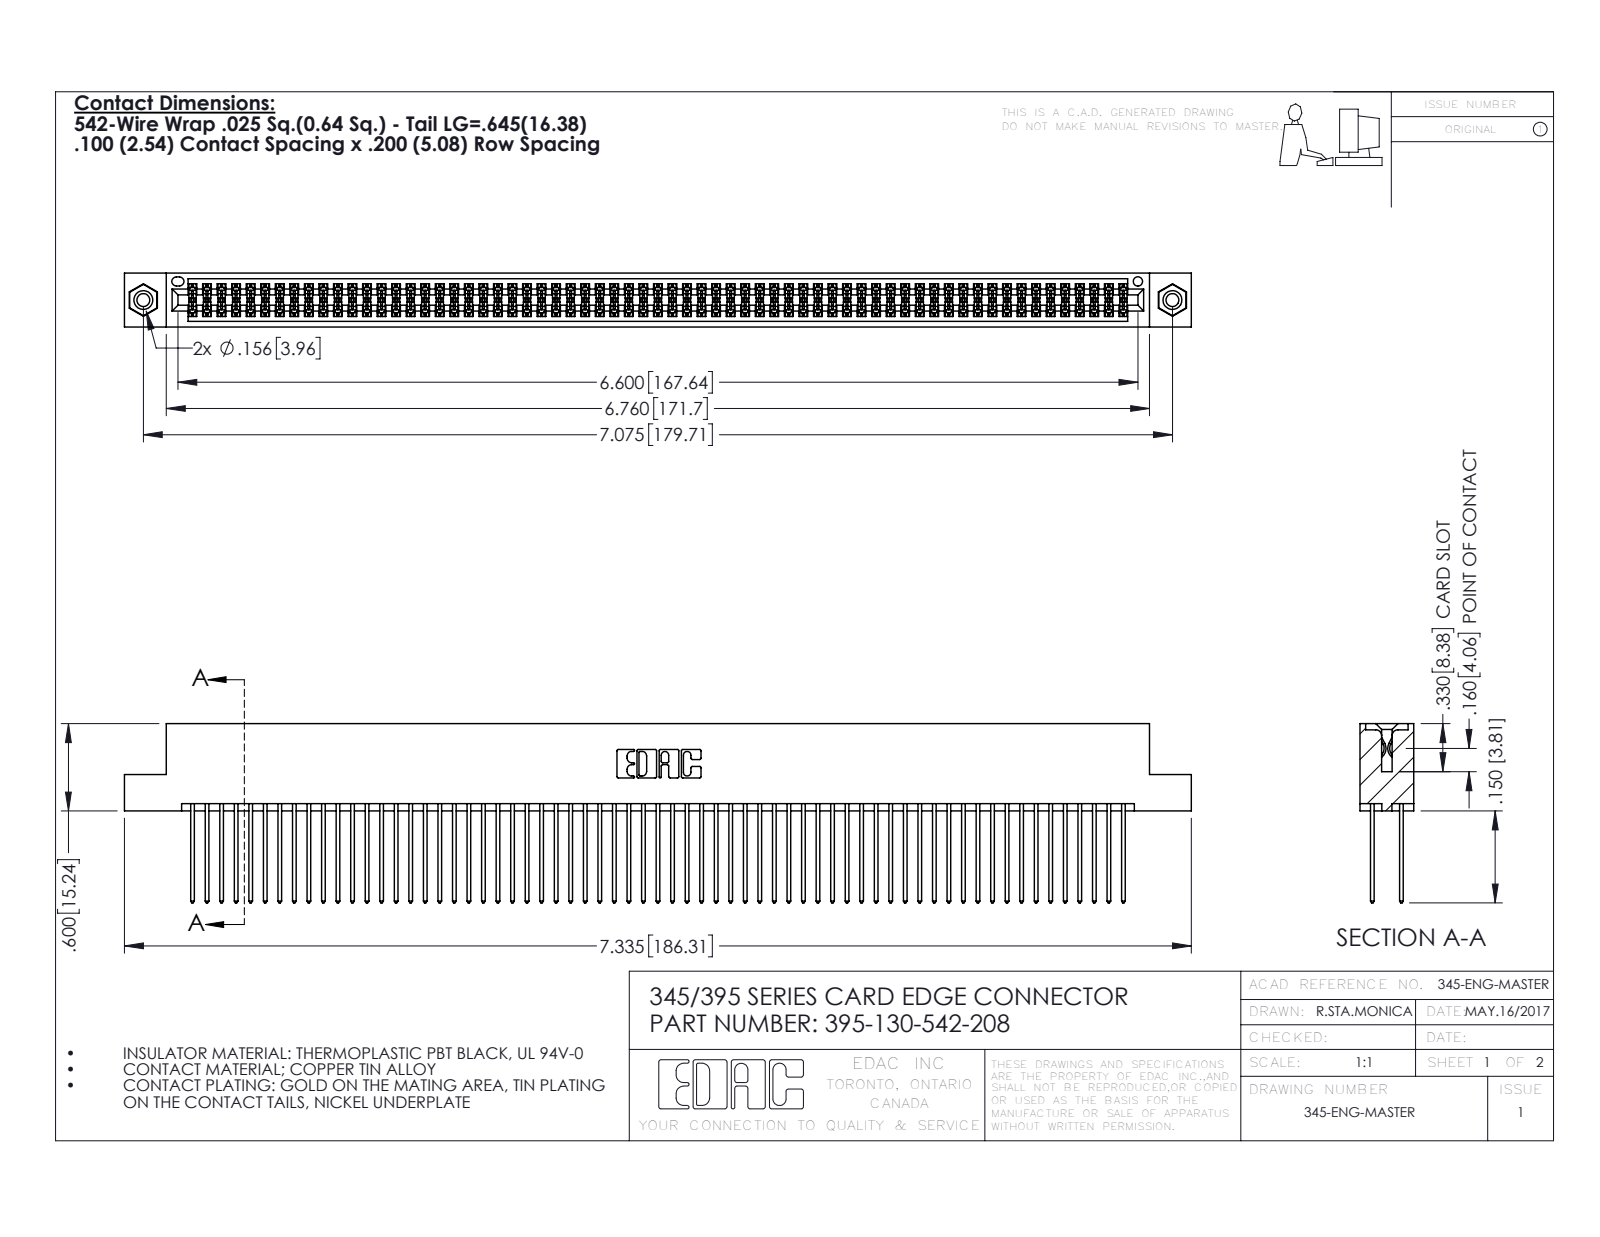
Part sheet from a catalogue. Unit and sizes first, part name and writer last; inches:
Units: inches
Overall size (bounding box): 7.335 × 1.232 × 0.37
Round holes (diameter × count): ⌀0.089 ×2, ⌀0.125 ×2, ⌀0.156 ×2, ⌀0.064 ×1
Round bosses / shafts (diameter × count): ⌀0.155 ×2
Partial cylindrical surfaces — rounded edges, fillets, slot ends (radius × count): R0.006 ×195, R0.01 ×130, R0.01 ×22, R0.007 ×6, R0.031 ×6, R0.026 ×3, R0.014 ×2, R0.019 ×2
Main face-to-face distances: 0.072, 0.298, 0.2, 0.098, 0.272, 0.025, 0.225, 0.37, 0.175, 0.149
Hole centre spacings: 0.27, 6.839, 7.075
Volume: 1.154 in³ · Surface area: 48.43 in²
Bodies: 133 solids, 6686 faces (4402 planar, 2268 cylindrical, 16 other)
Part name (STEP PRODUCT): 345-292-001_345-293-142; 345-250-001_345-250-003-102; 345 Part_Flush Mounting Lugs - 0.156 Dia-TI; 395-130-542-208
STEP written by: SolidWorks 2016 (CONFIG_CONTROL_DESIGN)
